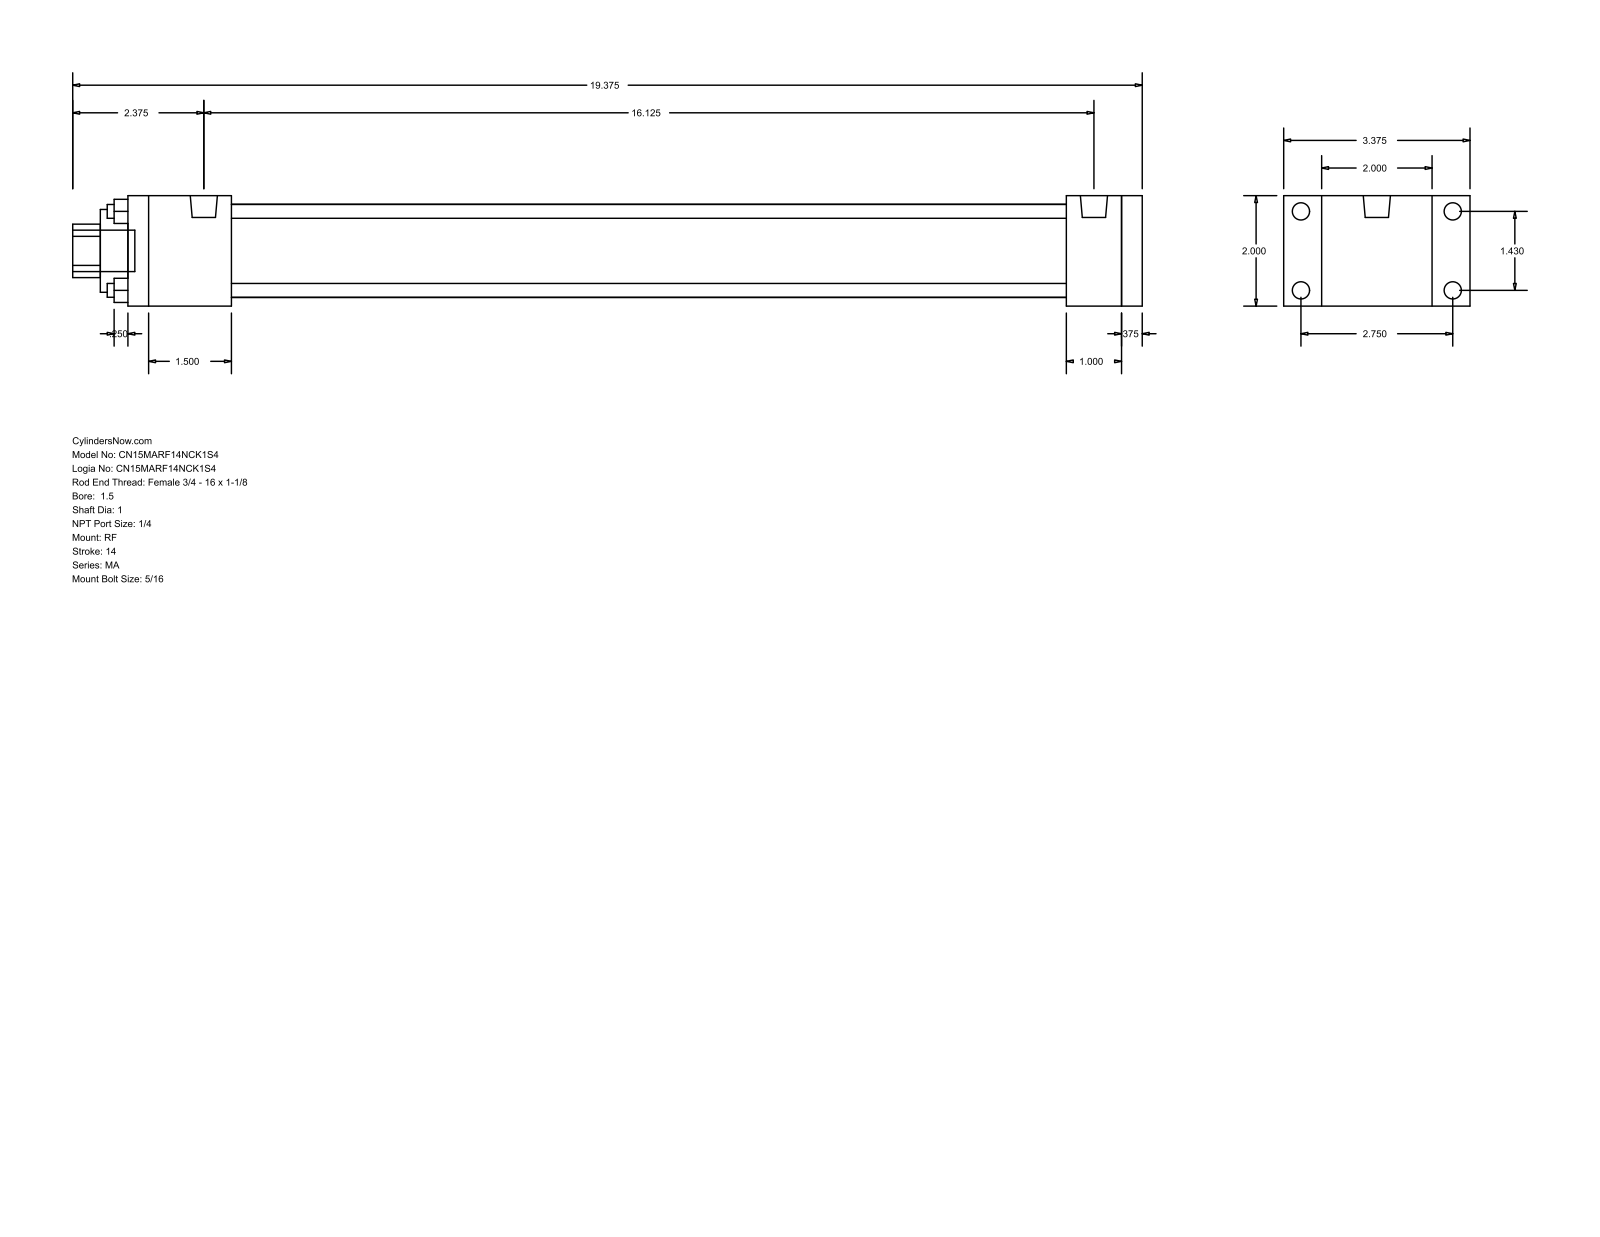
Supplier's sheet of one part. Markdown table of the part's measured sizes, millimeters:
| quantity | value |
| --- | --- |
| part name | MA_RF__0150_1 |
| STEP written by | GSSL Pune (CONFIG_CONTROL_DESIGN) |
| units | millimeters |
| bodies | 0 solids, 92 faces (64 planar, 28 cylindrical, 0 other) |
| overall size | 492.12 × 85.72 × 50.8 |
| round holes (diameter × count) | 6.35 × 4, 25.4 × 1, 38.1 × 1, 42.93 × 1 |
| round bosses / shafts (diameter × count) | 7.94 × 8, 12.49 × 2, 19.05 × 1 |
| partial cylindrical surfaces (radius × count) | 12.29 × 1 |
| main face-to-face distances | 50.8, 9.52, 466.72, 457.2, 25.4, 431.8, 34.92, 47.63, 384.17, 409.57 |
| hole center spacings | 25.68, 36.32, 51.36 |
